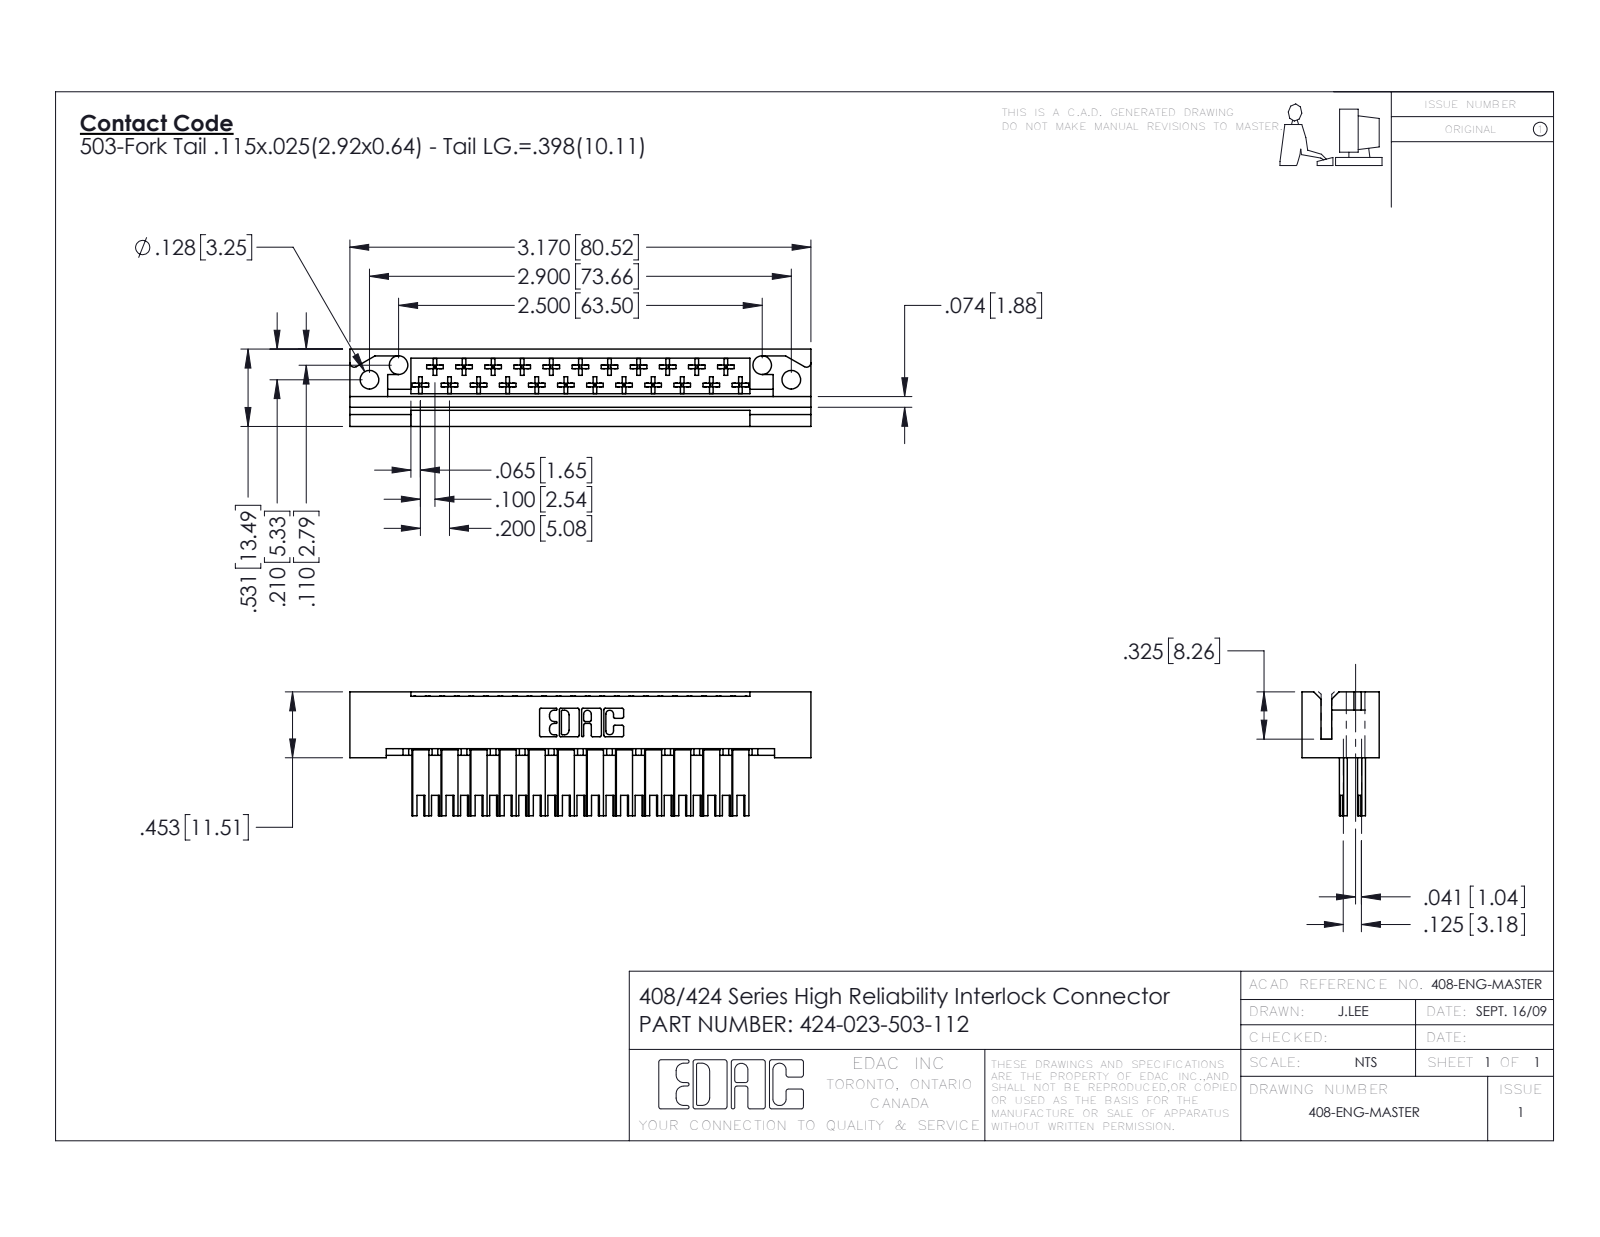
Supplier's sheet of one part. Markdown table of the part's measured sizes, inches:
| quantity | value |
| --- | --- |
| part name | 408-290-001_408-290-103; 424-023-503-112; 424 Part_023 |
| STEP written by | SolidWorks 2016 (CONFIG_CONTROL_DESIGN) |
| units | inches |
| bodies | 24 solids, 1364 faces (1032 planar, 240 cylindrical, 92 other) |
| overall size | 3.17 × 0.851 × 0.531 |
| volume | 0.553 in³ |
| surface area | 18.25 in² |
| round holes (diameter × count) | 0.128 × 4 |
| partial cylindrical surfaces (radius × count) | 0.01 × 138, 0.02 × 25, 0.01 × 22, 0.007 × 6, 0.031 × 6, 0.026 × 3, 0.03 × 2 |
| main face-to-face distances | 0.4, 0.025, 0.531, 0.125, 0.1, 0.131, 0.326, 0.074, 0.205, 0.091 |
| hole center spacings | 0.224, 2.702, 2.5, 2.9 |
